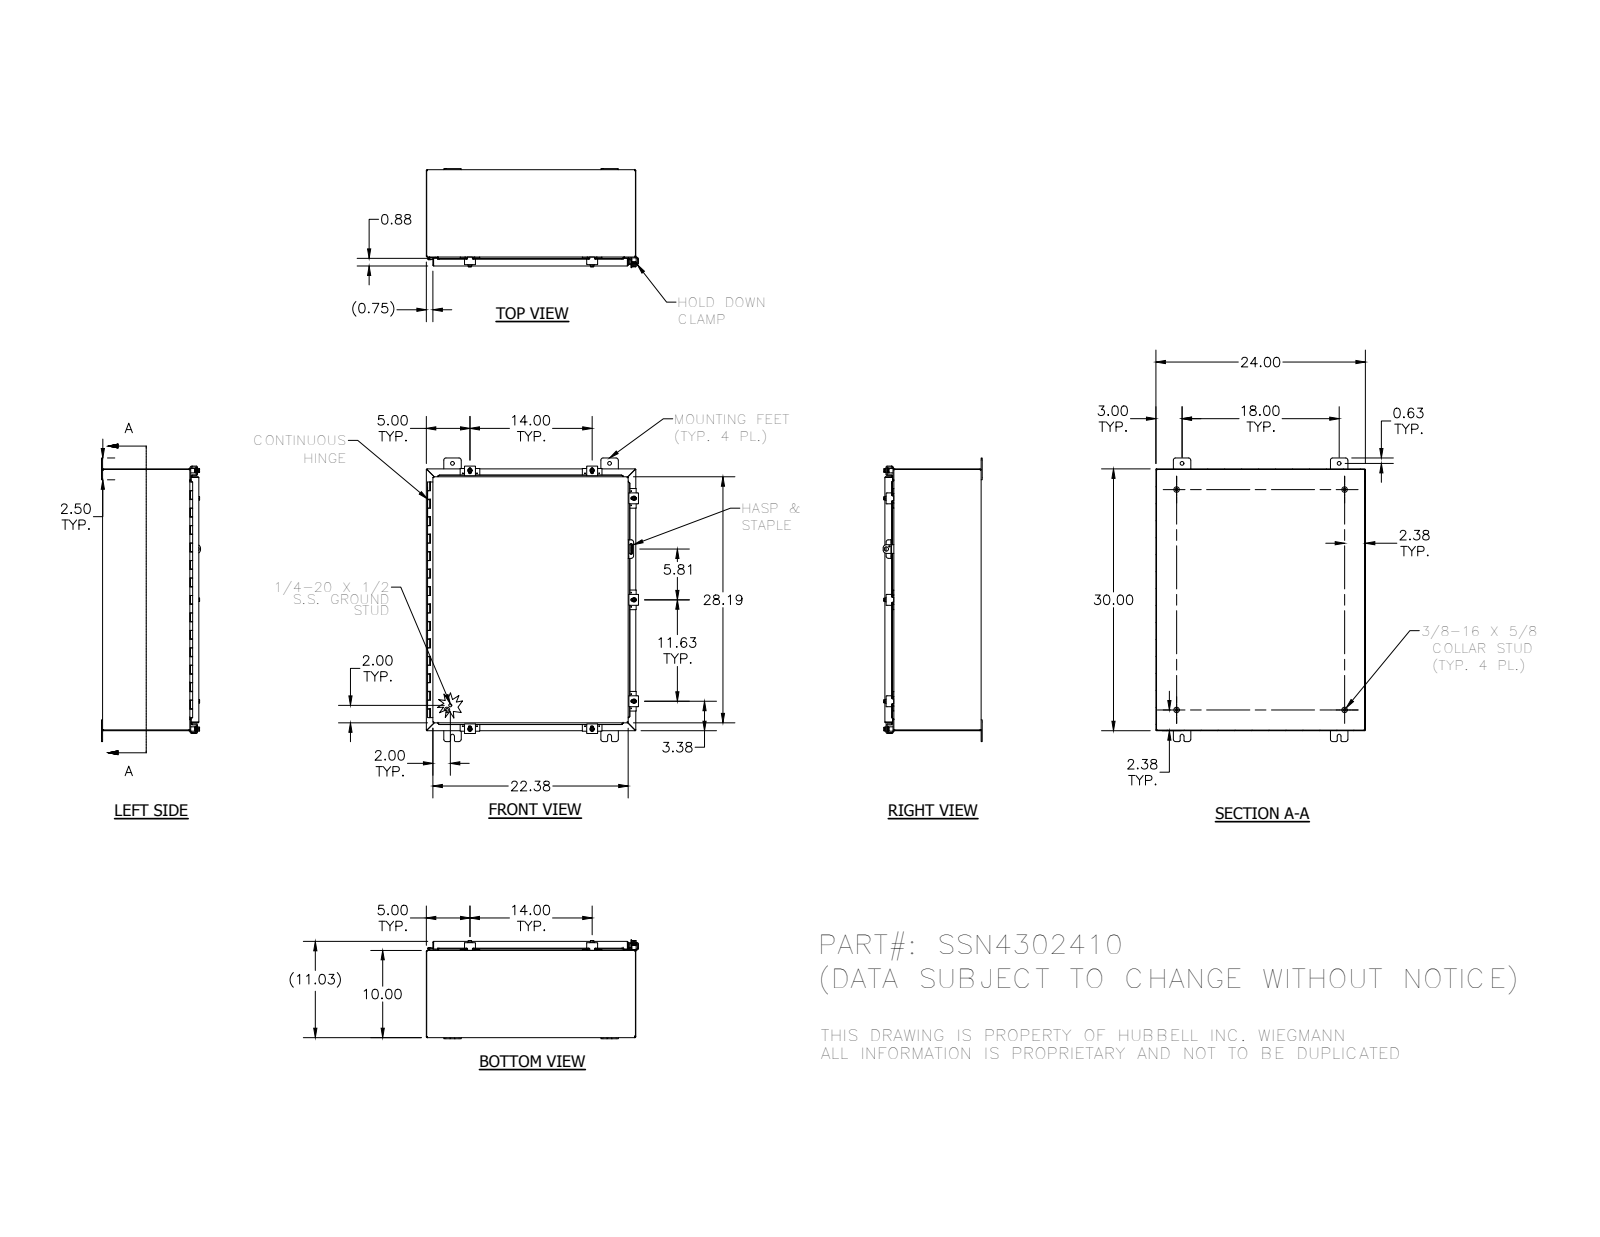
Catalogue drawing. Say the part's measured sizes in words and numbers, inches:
The part is named "HFW30825-3; 32912; SSN43024LID; 38412 (+8 more)". Its 3-D file was written by "SolidWorks 2014 (AUTOMOTIVE_DESIGN)". It is 52 solids with 2111 faces: 805 planar, 935 cylindrical and 371 other. Overall it measures 32.5 by 24.311 by 11.355 inches. Its volume is 224 cubic inches and its surface area 5 902 square inches. Round holes: 14 of diameter 0.11, 7 of diameter 0.211, 7 of diameter 0.281, 7 of diameter 0.3, 4 of diameter 0.438, 1 of diameter 0.125, 1 of diameter 0.156, 1 of diameter 0.5. Round bosses or shafts: 9 of diameter 0.25, 7 of diameter 0.52, 7 of diameter 0.5, 7 of diameter 0.35, 4 of diameter 0.625, 4 of diameter 0.33, 2 of diameter 0.115, 1 of diameter 0.337. Partial cylindrical surfaces (rounded edges, fillets, slot ends): 83 of radius 0.03, 37 of radius 0.125, 33 of radius 0.25, 23 of radius 0.031, 23 of radius 0.105, 15 of radius 0.062, 14 of radius 0.141, 10 of radius 0.1. The main face-to-face distances are 0.074, 10.959, 10.885, 11.033, 23.926, 29.926, 23.852, 24, 9.926, 1.033. The hole center spacings are 0.876, 29.3, 14, 1.625, 13.191, 14.816, 28.961, 29.006.
